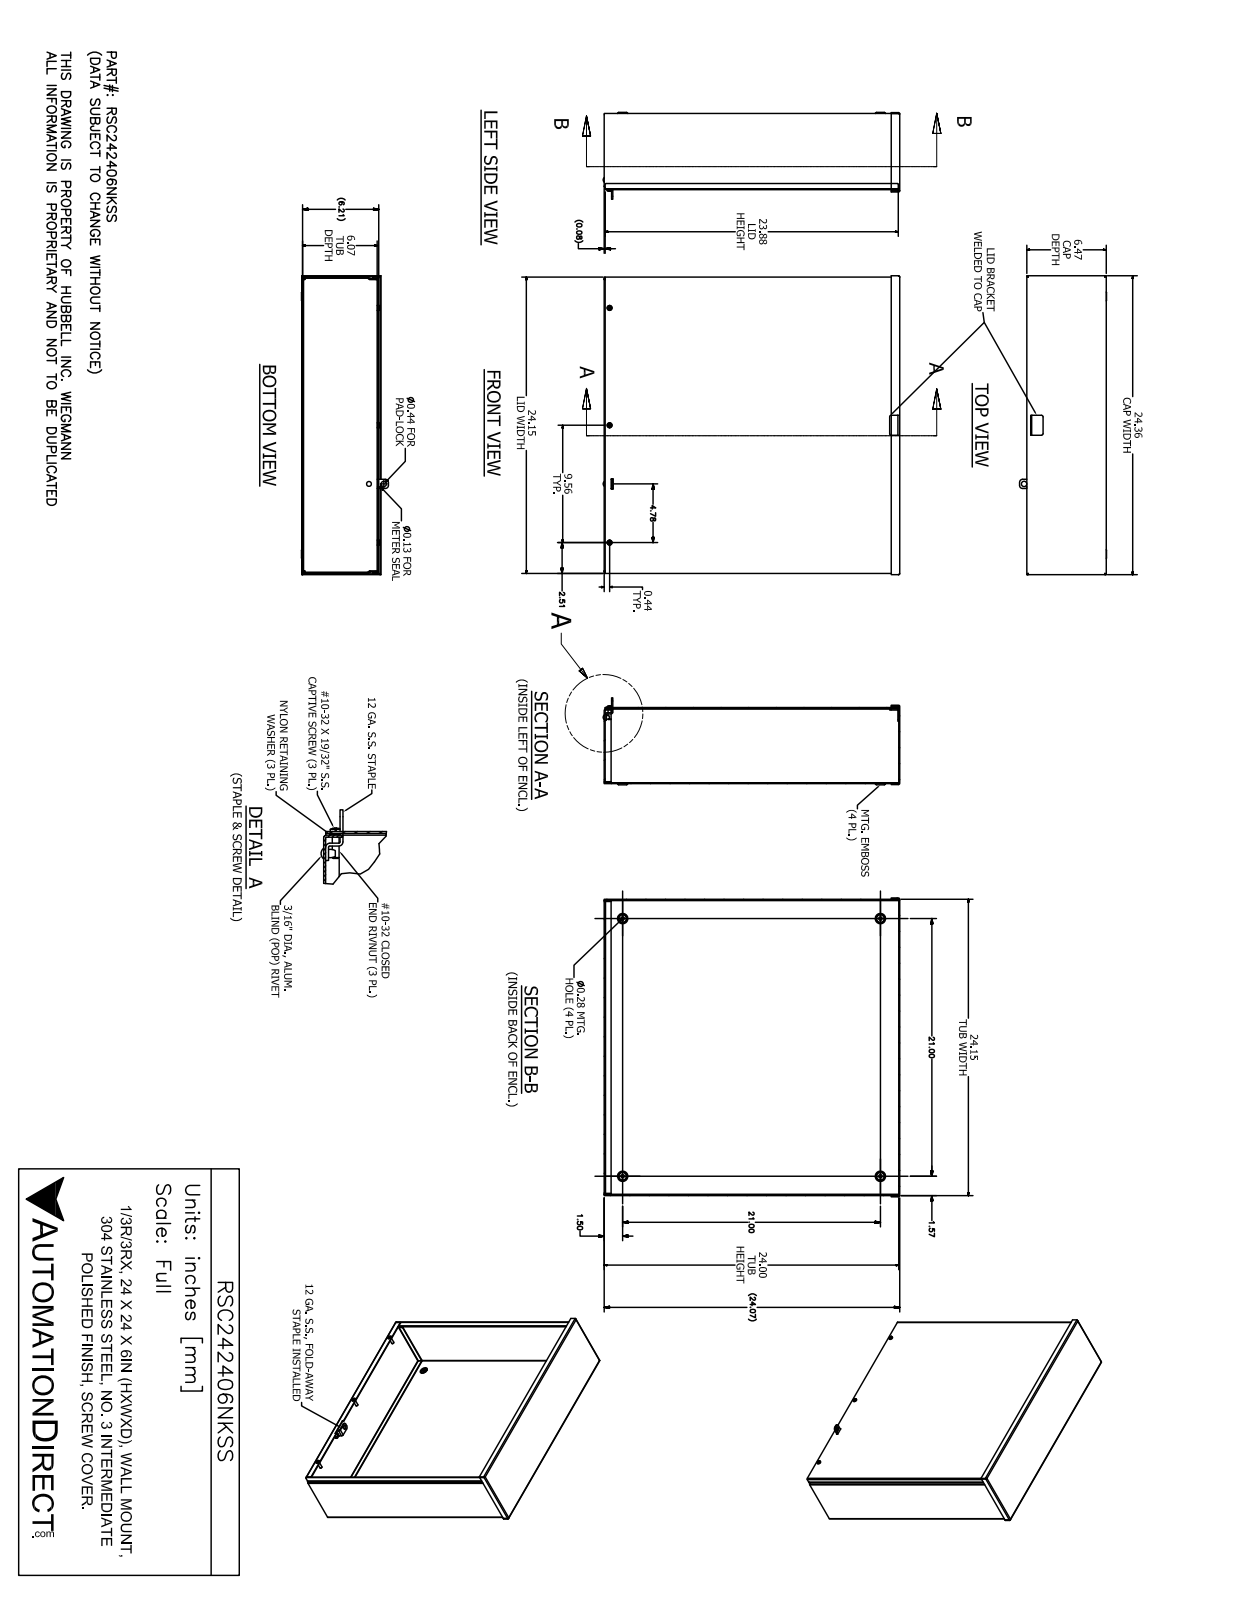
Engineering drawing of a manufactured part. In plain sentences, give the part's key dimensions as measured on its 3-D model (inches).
The part is named "RSC242406NKSS". Its 3-D file was written by "SolidWorks 2017 (AUTOMOTIVE_DESIGN)". It is 16 solids with 458 faces: 237 planar, 113 cylindrical and 108 other. Overall it measures 24.359 by 24.164 by 7.084 inches. Its volume is 135.9 cubic inches and its surface area 3 701 square inches. Round holes: 6 of diameter 0.25, 4 of diameter 0.281, 3 of diameter 0.156, 3 of diameter 0.196, 3 of diameter 0.257, 3 of diameter 0.278, 1 of diameter 0.125, 1 of diameter 0.198, 1 of diameter 0.201, 1 of diameter 0.437. Round bosses or shafts: 3 of diameter 0.453, 3 of diameter 0.406, 3 of diameter 0.248, 3 of diameter 0.167, 1 of diameter 0.187. Partial cylindrical surfaces (rounded edges, fillets, slot ends): 23 of radius 0.031, 17 of radius 0.105, 4 of radius 0.125, 4 of radius 0.25, 3 of radius 0.062, 3 of radius 0.089, 2 of radius 0.047, 2 of radius 0.05. The main face-to-face distances are 0.074, 6.132, 6.206, 6.058, 24, 24.074, 23.926, 24.148, 0.115, 23.959. The hole center spacings are 9.563, 21, 25.053, 23.156, 1.417, 1.441, 10.554, 10.557.
